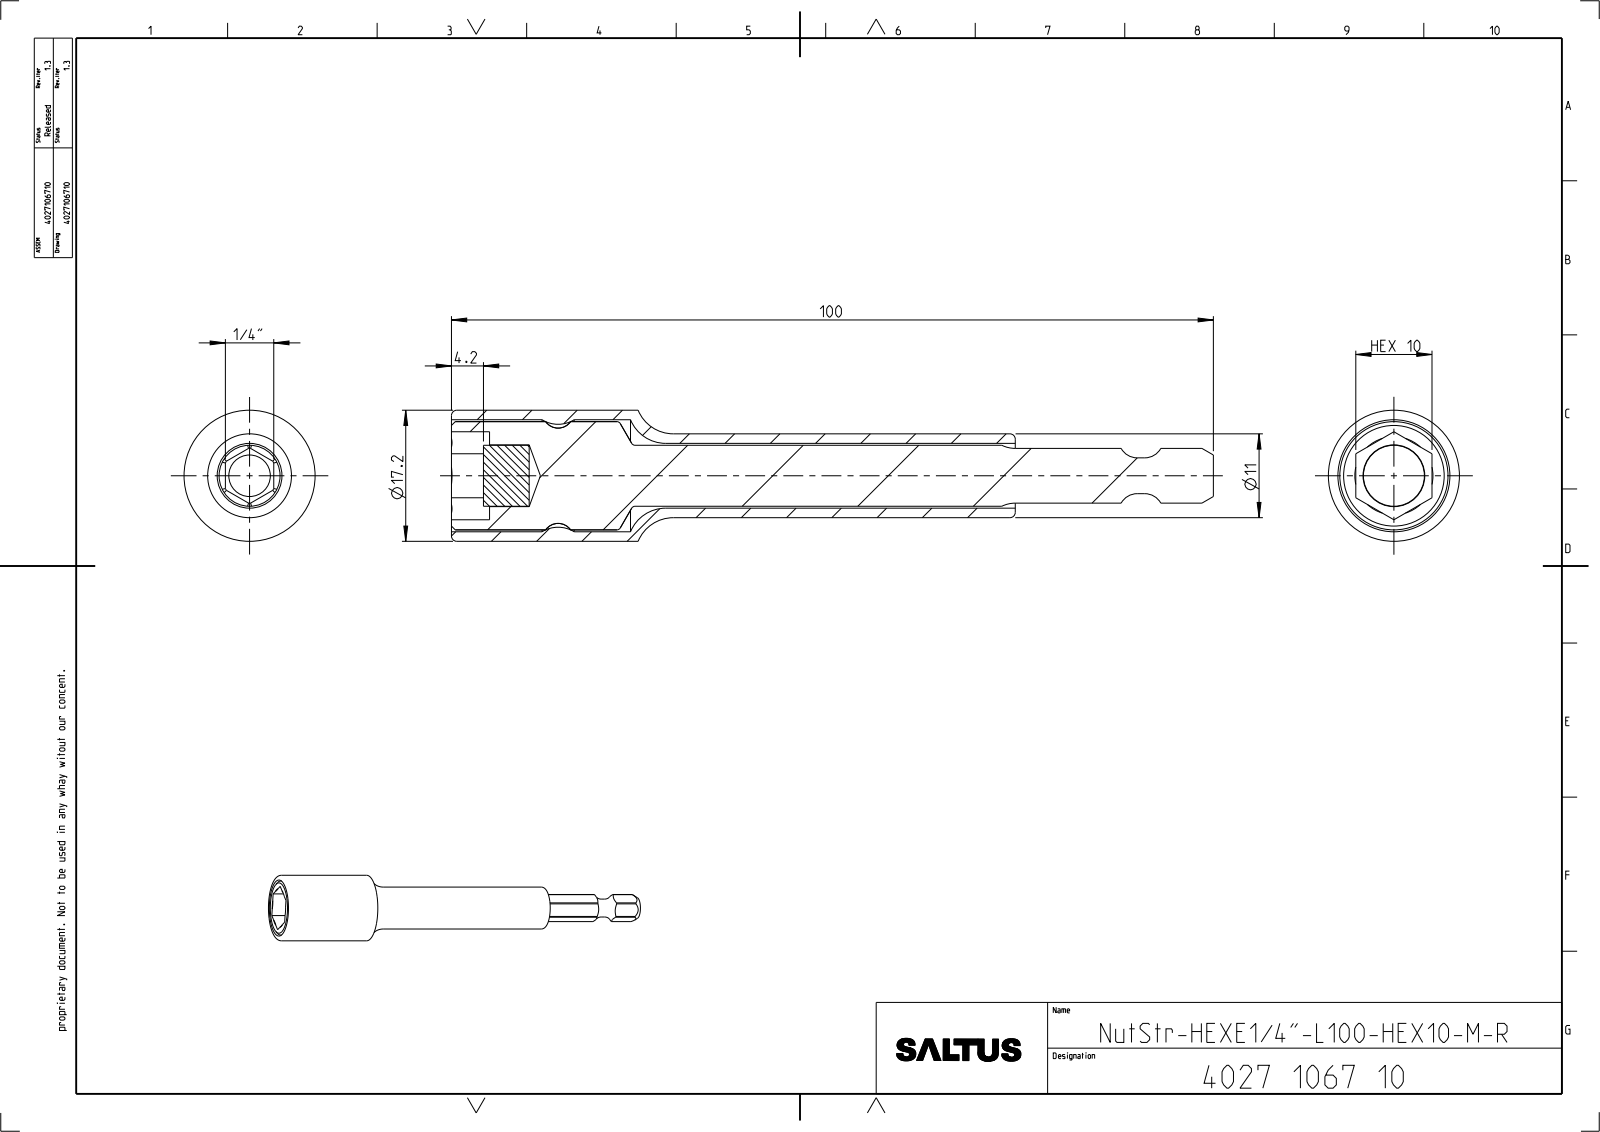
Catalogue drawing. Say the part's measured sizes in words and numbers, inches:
The part is named "4027904292; 4027299440; MAGNET_FLEXIBLE_TEMPLATE_AF4; 4027106710_ASM". Its 3-D file was written by "CREO PARAMETRIC BY PTC INC, 2022414 (CONFIG_CONTROL_DESIGN)". It is 4 solids with 118 faces: 28 planar, 42 cylindrical and 48 other. Overall it measures 3.937 by 0.677 by 0.677 inches. Its volume is 0.644 cubic inches and its surface area 15.04 square inches. Round holes: 1 of diameter 0.319, 1 of diameter 0.335, 1 of diameter 0.579. Round bosses or shafts: 1 of diameter 0.677, 1 of diameter 0.559, 1 of diameter 0.433, 1 of diameter 0.315, 1 of diameter 0.185. Partial cylindrical surfaces (rounded edges, fillets, slot ends): 6 of radius 0.157, 1 of radius 0.141. The main face-to-face distances are 0.25, 0.236, 0.072, 0.322, 0.394, 0.322, 0.072, 0.402, 0.165, 0.602.
